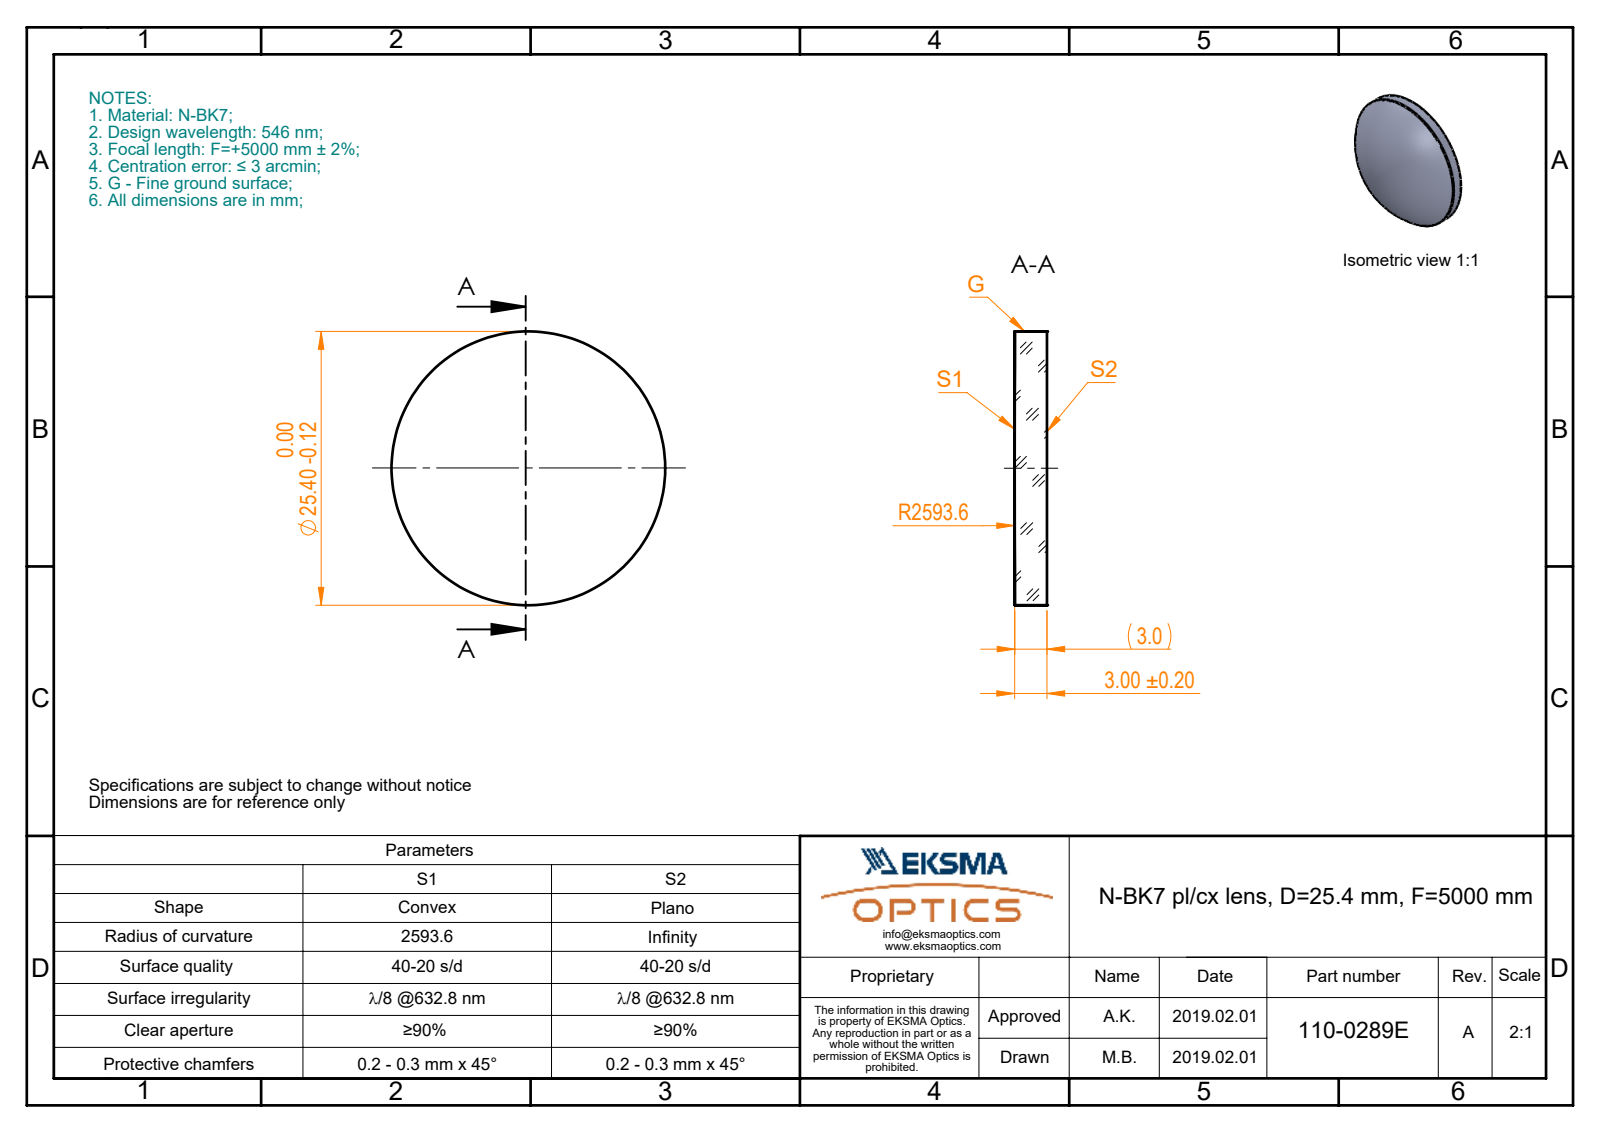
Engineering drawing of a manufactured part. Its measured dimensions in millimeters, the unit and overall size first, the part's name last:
Units: millimetres
Overall size (bounding box): 25.4 × 25.4 × 3
Round bosses / shafts (diameter × count): ⌀25.4 ×1
Volume: 1 512 mm³ · Surface area: 1 250 mm²
Bodies: 1 solid, 5 faces (1 planar, 2 cylindrical, 2 other)
Part name (STEP PRODUCT): 110-0289E BK7 pl-cx 25.4 F5000
STEP written by: SolidWorks 2017 (CONFIG_CONTROL_DESIGN)
